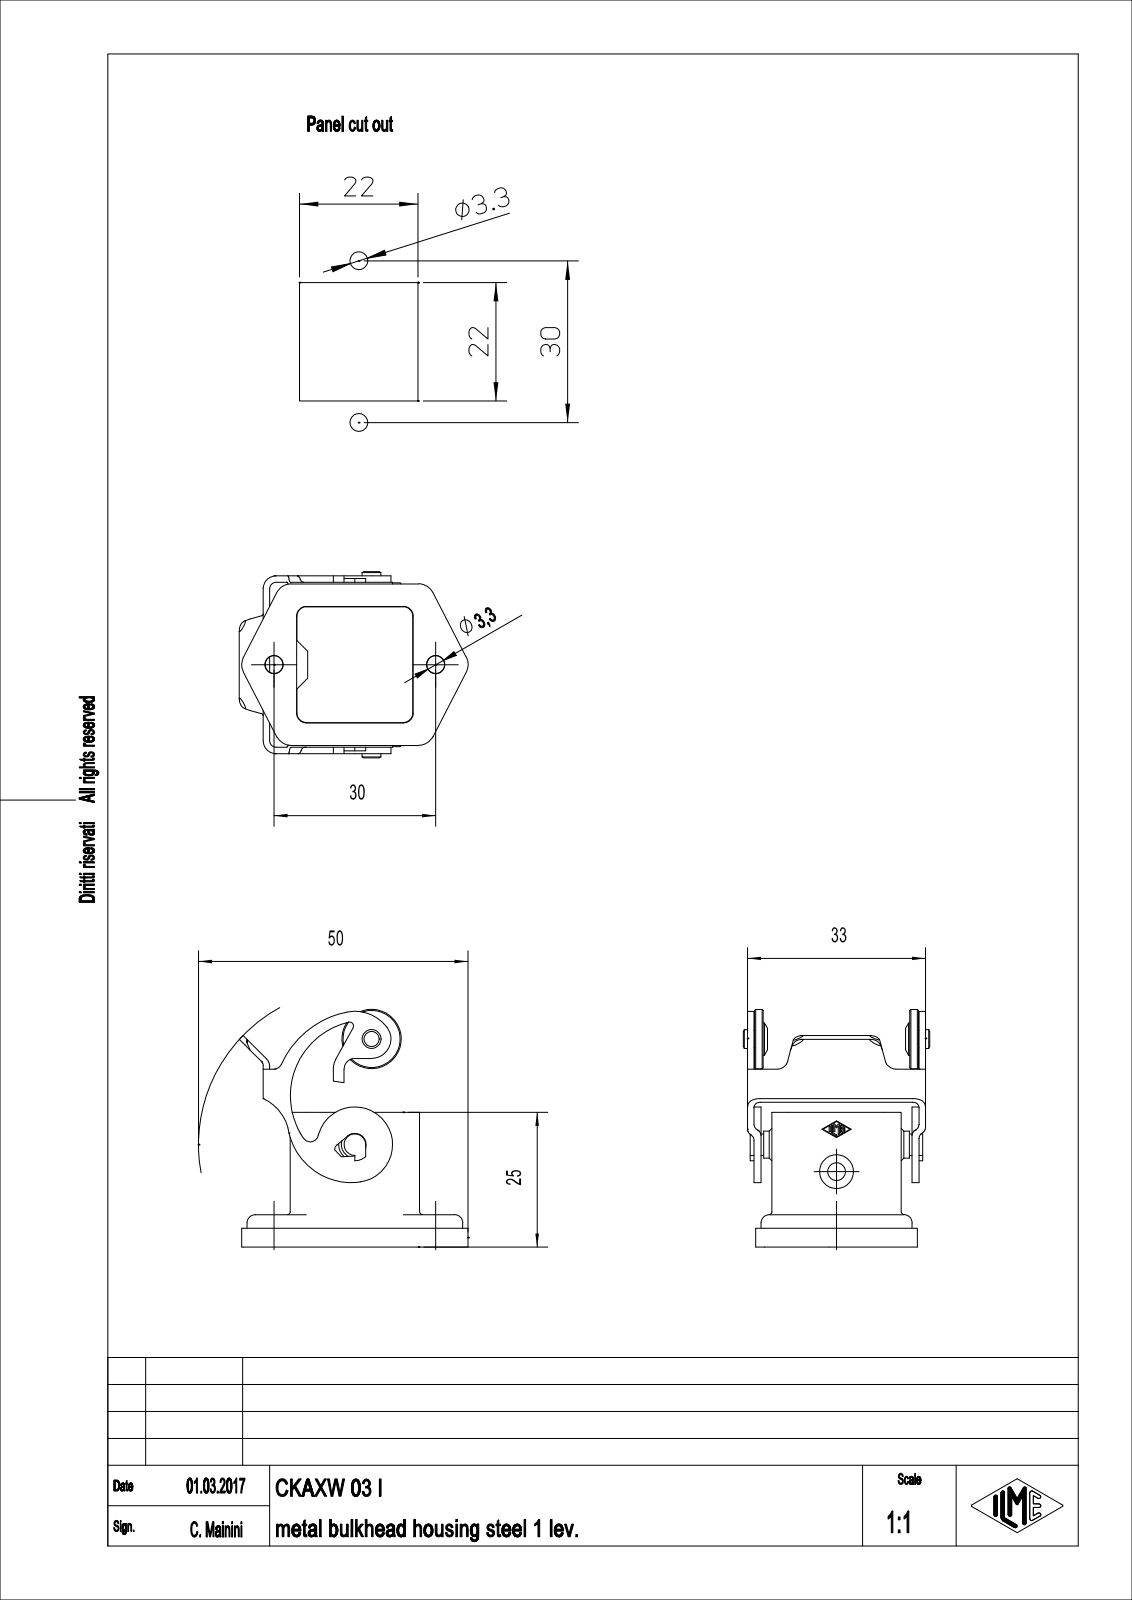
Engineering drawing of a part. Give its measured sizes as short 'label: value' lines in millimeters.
name: CKAXW 03 I
written by: Autodesk Inventor 7 (AUTOMOTIVE_DESIGN)
unit: mm
bodies: 1 solid, 314 faces (115 planar, 135 cylindrical, 64 other)
size: 44.1 × 42.45 × 34.6
volume: 6 918 mm³; area: 8 675 mm²
holes: 3× ⌀3.3, 2× ⌀3.4
bosses: 1× ⌀11, 1× ⌀6, 1× ⌀5, 1× ⌀4, 1× ⌀3.5, 1× ⌀3.2
rounds: 14× R0.25, 11× R2, 11× R3, 8× R1.2, 8× R1.5, 8× R1.75, 4× R0.5, 2× R2.4
face distances: 1.25, 22.75, 21.5, 24, 1.2, 2, 3.25, 26, 2.5, 24.75
hole spacings: 30
